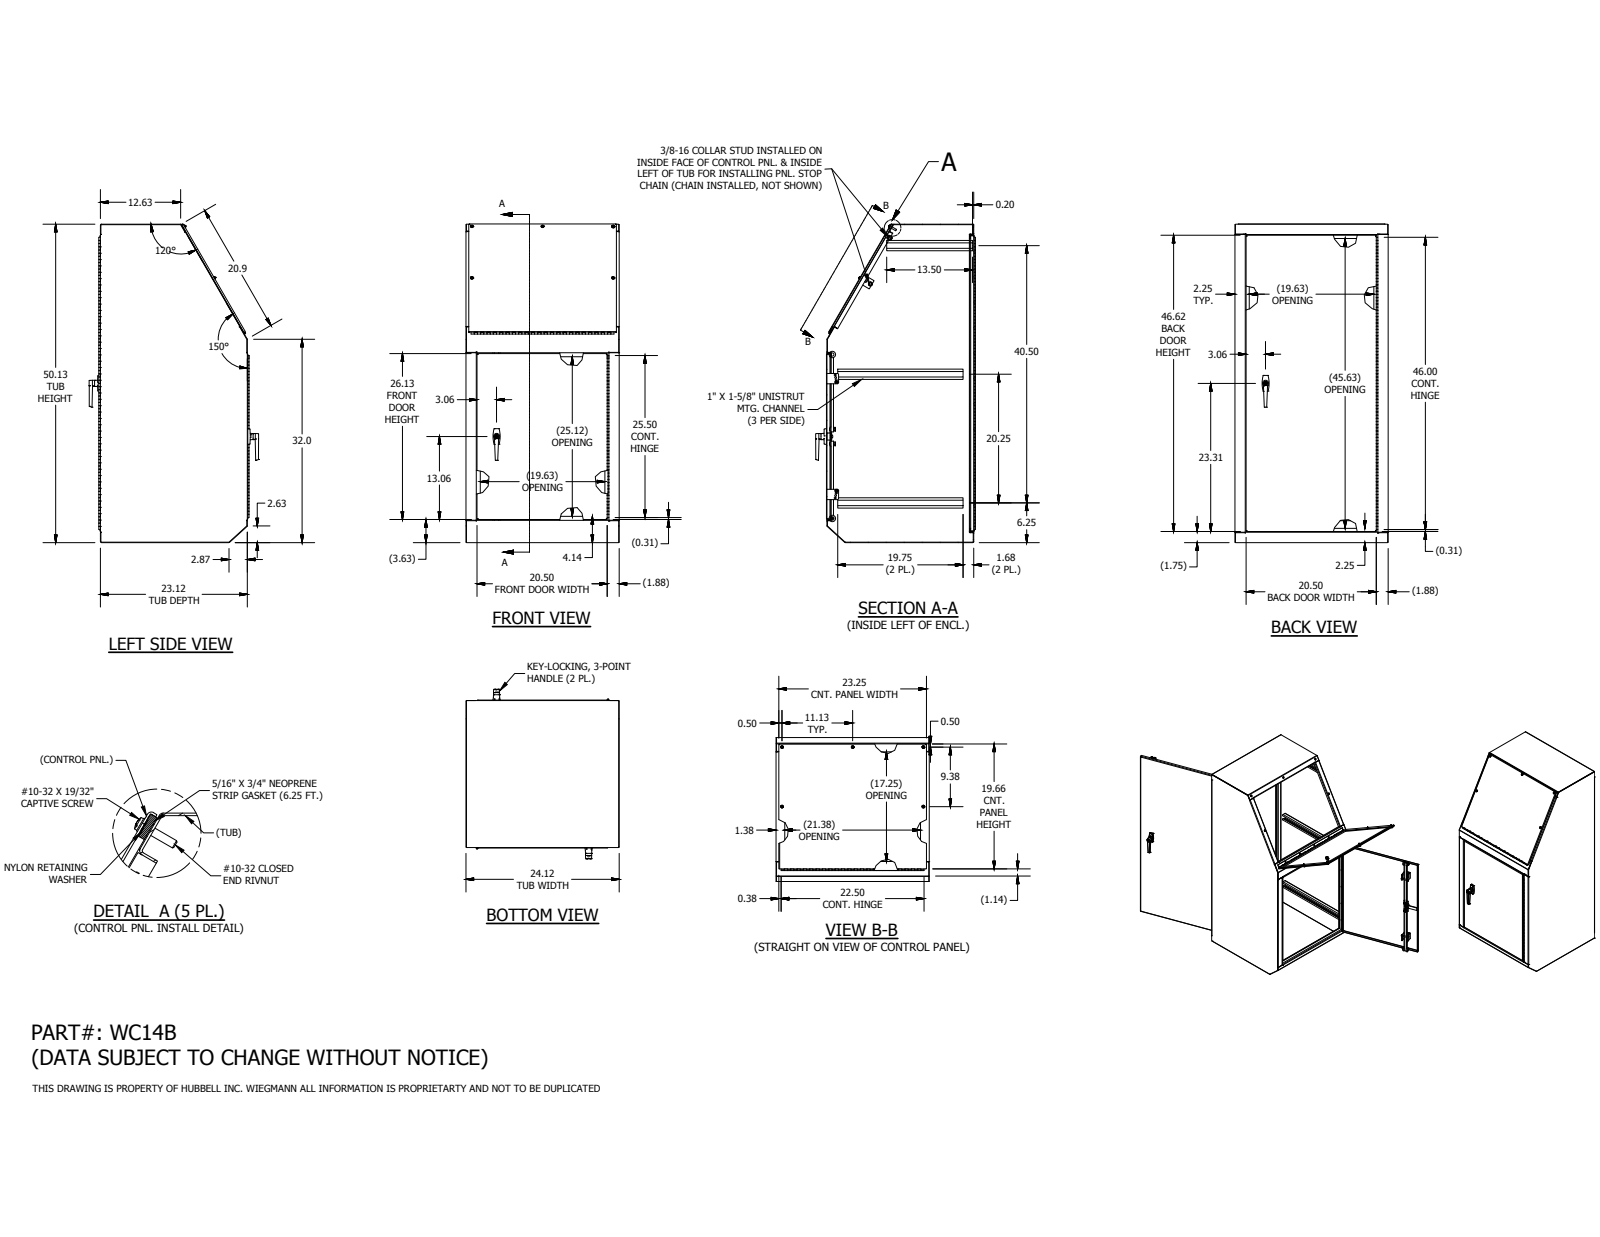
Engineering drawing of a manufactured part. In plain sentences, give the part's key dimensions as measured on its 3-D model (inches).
The part is named "WC14B". Its 3-D file was written by "SolidWorks 2019 (AUTOMOTIVE_DESIGN)". It is 101 solids with 4437 faces: 2451 planar, 1283 cylindrical and 703 other. Overall it measures 50.156 by 26.679 by 24.125 inches. Its volume is 537.7 cubic inches and its surface area 14 002 square inches. Round holes: 22 of diameter 0.313, 16 of diameter 0.277, 10 of diameter 0.083, 9 of diameter 0.25, 8 of diameter 0.2, 5 of diameter 0.156, 5 of diameter 0.188, 5 of diameter 0.196, 5 of diameter 0.257, 5 of diameter 0.278, 4 of diameter 0.159, 4 of diameter 0.241. Round bosses or shafts: 14 of diameter 0.157, 5 of diameter 0.453, 5 of diameter 0.437, 5 of diameter 0.406, 5 of diameter 0.248, 5 of diameter 0.167, 4 of diameter 1, 4 of diameter 0.563. Partial cylindrical surfaces (rounded edges, fillets, slot ends): 46 of radius 0.008, 43 of radius 0.136, 32 of radius 0.01, 31 of radius 0.062, 12 of radius 0.019, 12 of radius 0.024, 12 of radius 0.039, 12 of radius 0.053. The main face-to-face distances are 0.074, 0.074, 23.977, 23.199, 24.051, 24.051, 24.125, 23.125, 50.051, 23.273. The hole center spacings are 5, 10, 15, 0.293, 22.25, 0.201, 20, 24.144.
